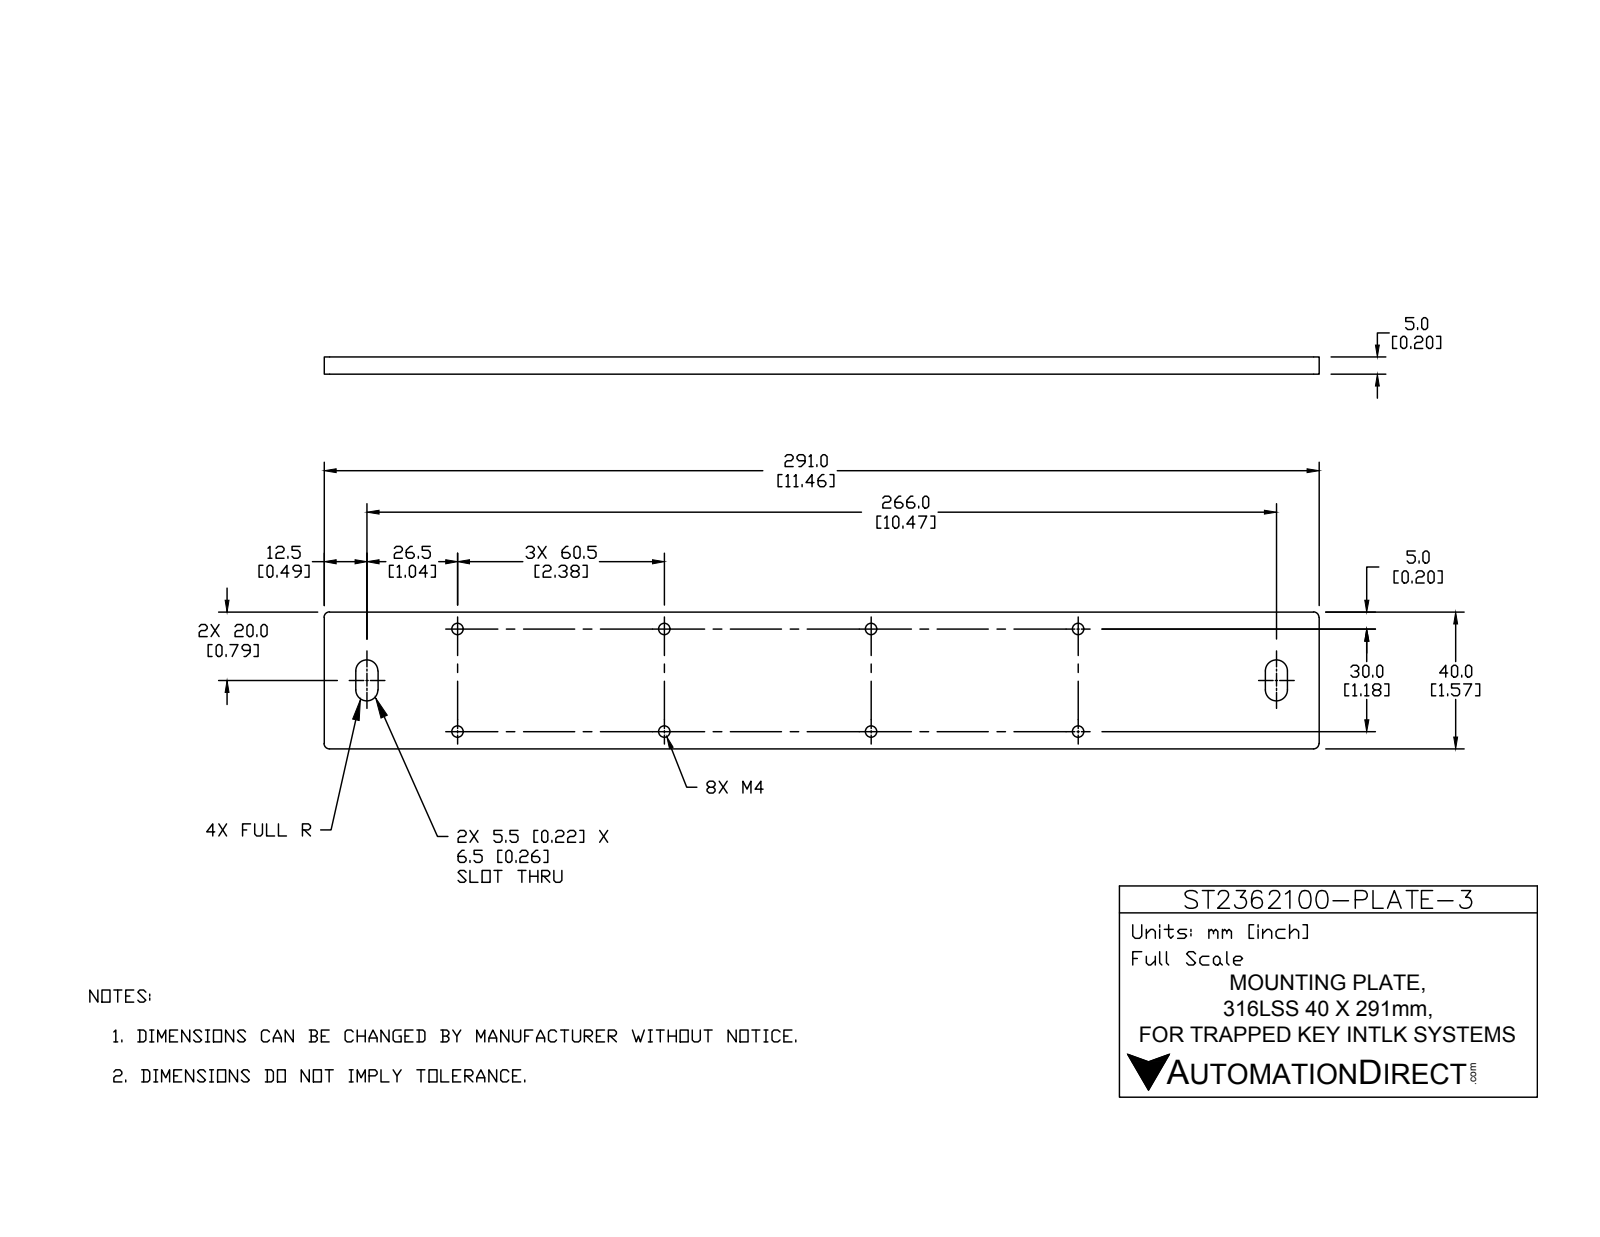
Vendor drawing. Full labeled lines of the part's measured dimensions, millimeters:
Part name (STEP PRODUCT): ST2362100-PLATE-3
STEP written by: SolidWorks 2017 (AUTOMOTIVE_DESIGN)
Units: millimetres
Bodies: 1 solid, 58 faces (10 planar, 32 cylindrical, 16 other)
Overall size (bounding box): 291 × 40 × 5
Volume: 57 090 mm³ · Surface area: 26 590 mm²
Round holes (diameter × count): ⌀3.3 ×8
Partial cylindrical surfaces — rounded edges, fillets, slot ends (radius × count): R0.2 ×8, R0.5 ×8, R2 ×4, R3.3 ×4
Main face-to-face distances: 5, 40, 291, 9.2, 15.7, 275.3, 281.8, 6.5, 266, 272.5
Hole centre spacings: 60, 67.1, 30, 120, 123.7, 180, 182.5
